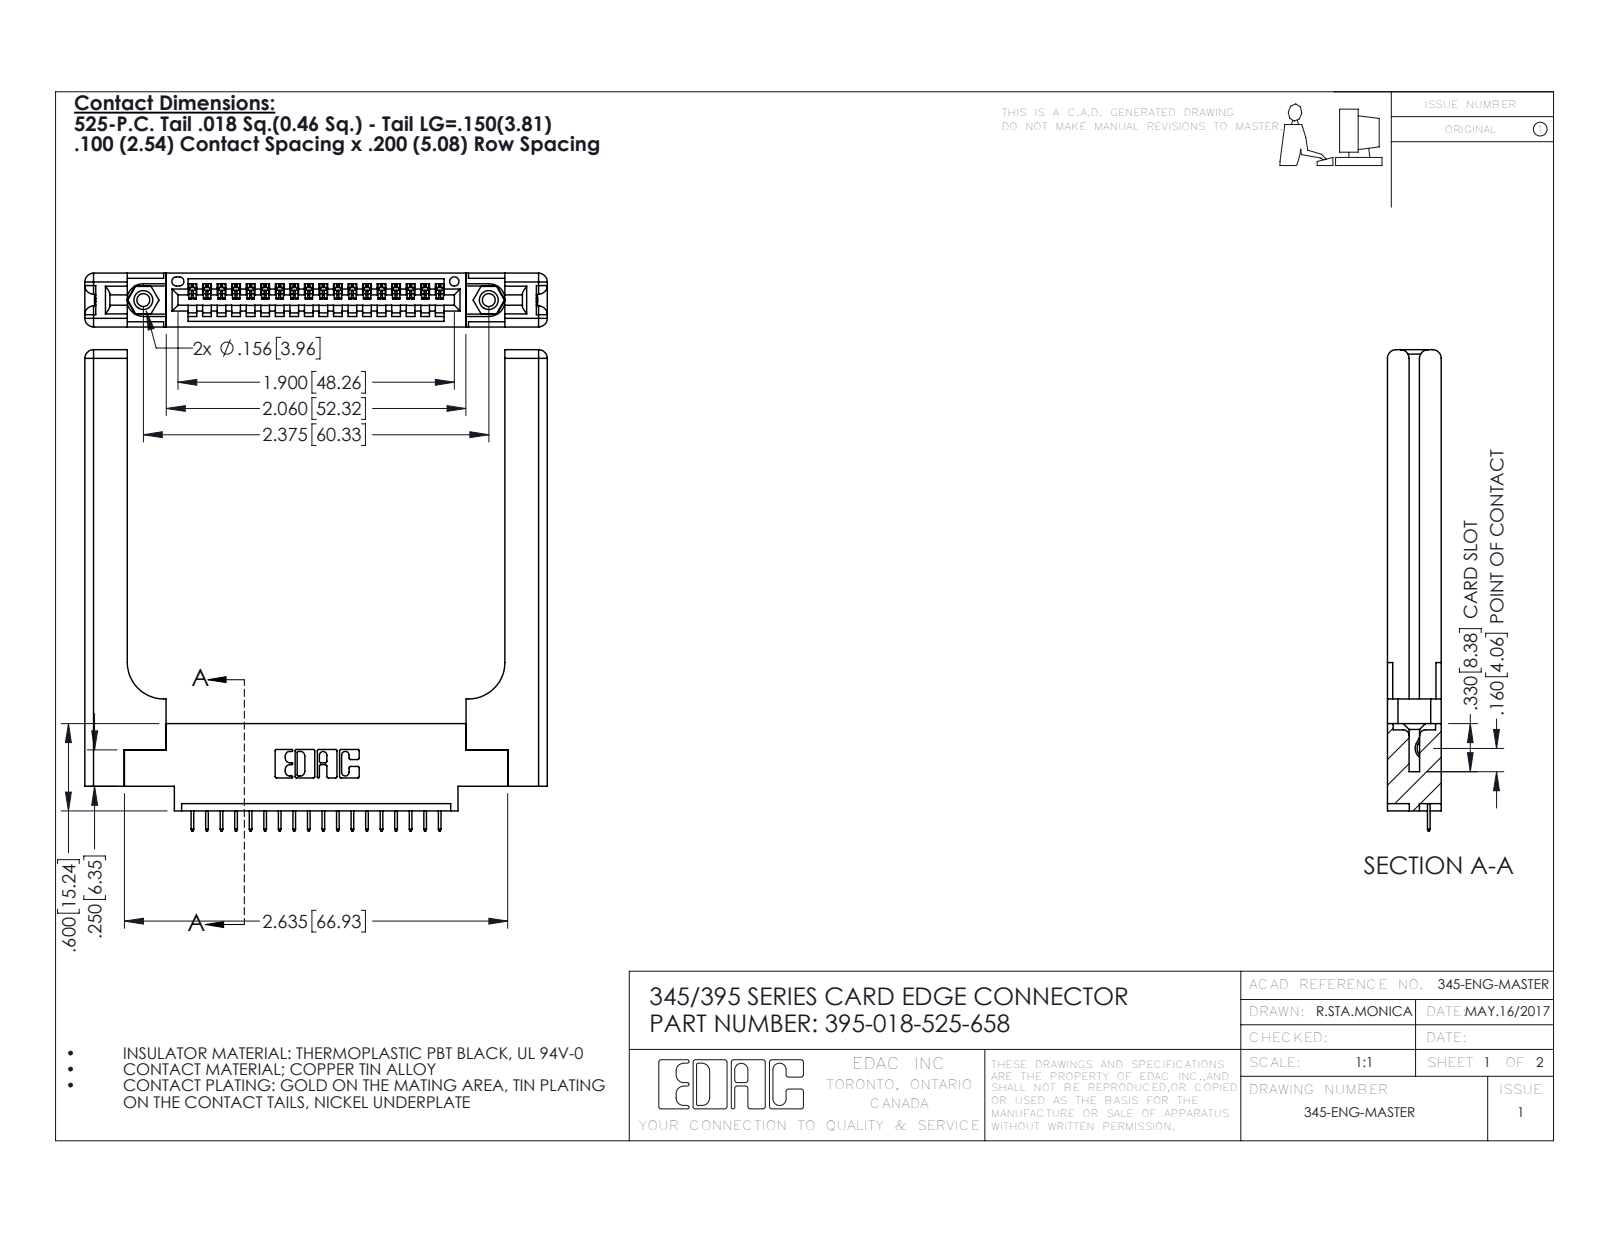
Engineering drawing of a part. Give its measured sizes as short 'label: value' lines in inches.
name: 395-018-525-658; 345-292-001_345-293-125; 345-220-058_345-220-058; 345 Part_0.170 Offset - 0.156 Dia-TH (+1 more)
written by: SolidWorks 2020 (CONFIG_CONTROL_DESIGN)
unit: in
bodies: 23 solids, 1502 faces (1060 planar, 382 cylindrical, 60 other)
size: 3.307 × 3.179 × 0.37
volume: 0.964 in³; area: 22.54 in²
holes: 2× ⌀0.089, 2× ⌀0.125, 2× ⌀0.156, 1× ⌀0.064
bosses: 2× ⌀0.155
rounds: 36× R0.006, 22× R0.01, 16× R0.06, 6× R0.007, 6× R0.031, 3× R0.026, 2× R0.03, 2× R0.031
face distances: 0.37, 0.072, 0.298, 0.15, 0.148, 0.077, 0.22, 0.123, 0.12, 0.098
hole spacings: 0.27, 2.141, 2.375
